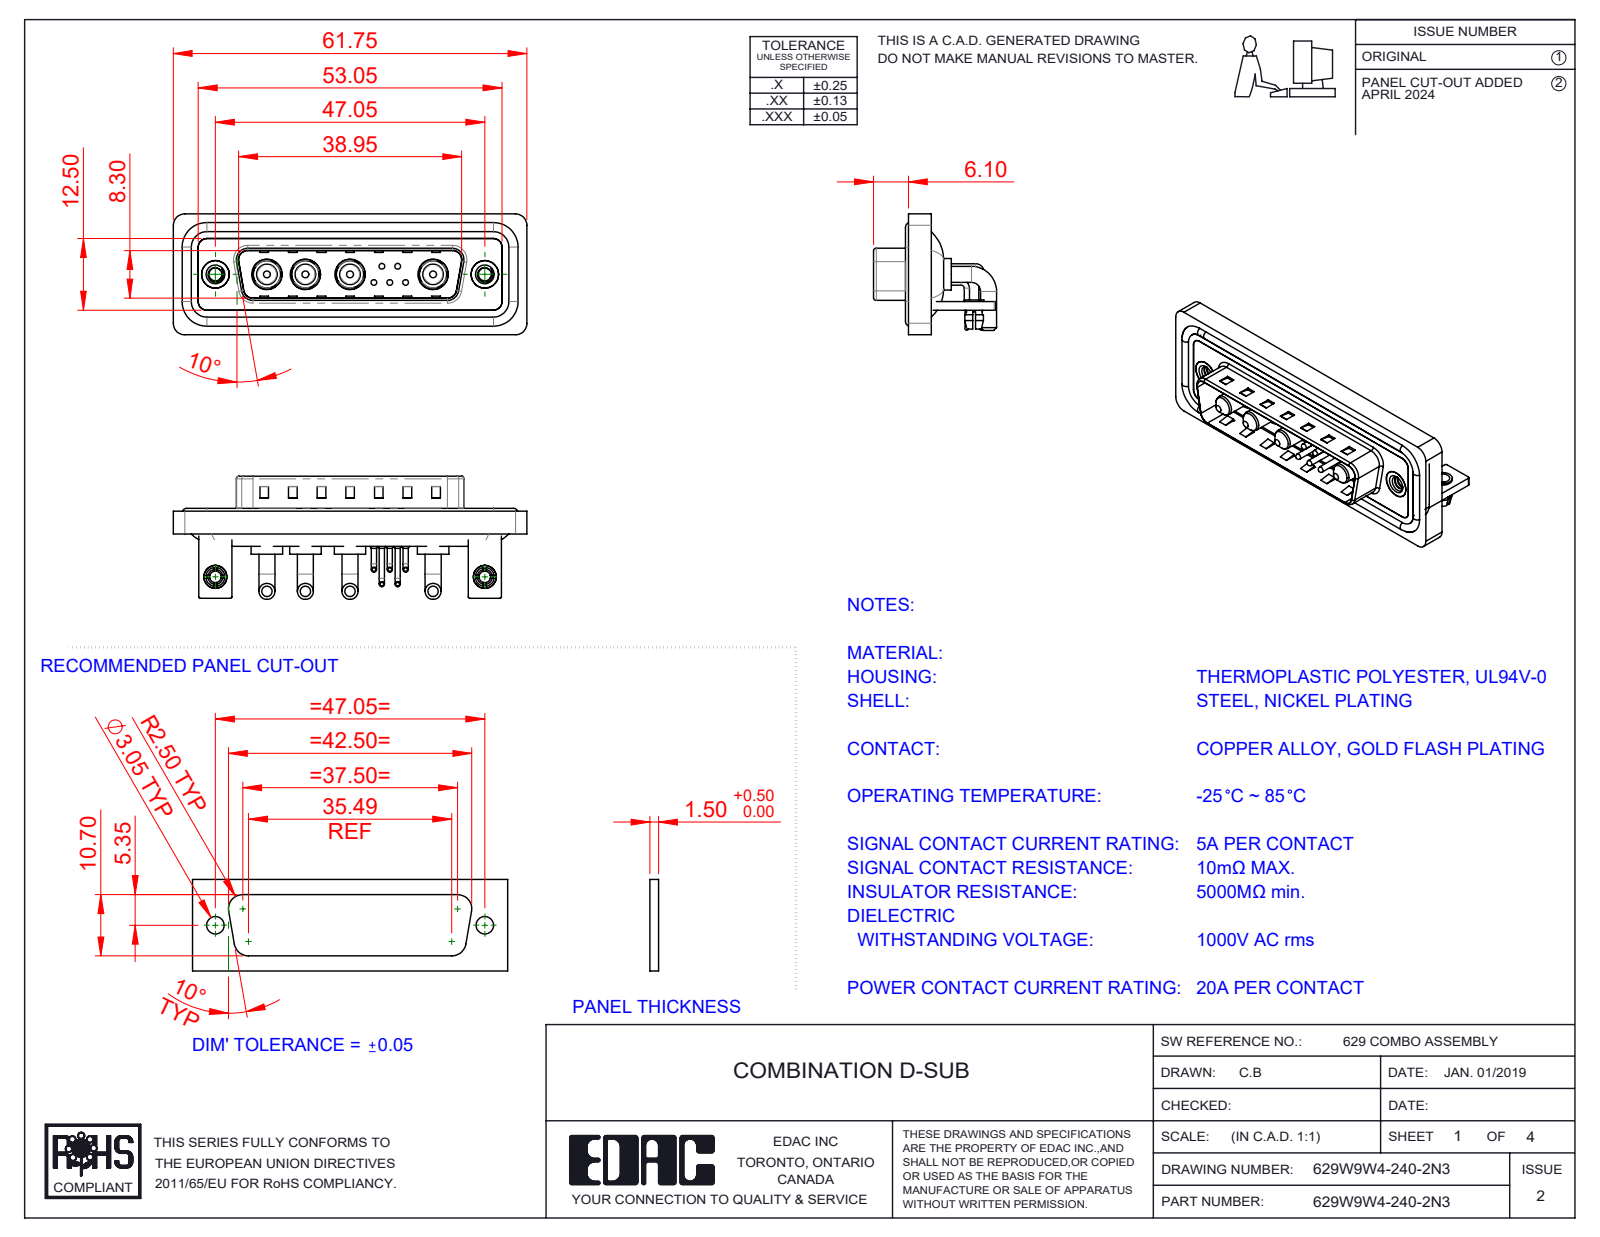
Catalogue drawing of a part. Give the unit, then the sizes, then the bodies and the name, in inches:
Units: inches
Overall size (bounding box): 2.431 × 0.846 × 0.831
Round holes (diameter × count): ⌀0.079 ×7, ⌀0.03 ×5, ⌀0.063 ×5, ⌀0.191 ×4, ⌀0.209 ×4, ⌀0.089 ×2, ⌀0.098 ×2, ⌀0.126 ×2, ⌀0.157 ×2, ⌀0.189 ×2, ⌀0.197 ×2
Round bosses / shafts (diameter × count): ⌀0.035 ×10, ⌀0.11 ×8, ⌀0.059 ×5, ⌀0.039 ×5, ⌀0.026 ×5, ⌀0.217 ×4, ⌀0.205 ×4, ⌀0.187 ×4
Partial cylindrical surfaces — rounded edges, fillets, slot ends (radius × count): R0.079 ×19, R0.059 ×18, R0.01 ×16, R0.02 ×9, R0.063 ×8, R0.04 ×5, R0.024 ×4, R0.026 ×4
Main face-to-face distances: 0.016, 0.059, 0.031, 0.114, 0.083, 0.043, 0.146, 0.161, 0.177, 0.063
Hole centre spacings: 0.124, 0.109, 0.198, 0.571, 1.852, 0.109, 0.173, 0.174
Volume: 0.489 in³ · Surface area: 20.42 in²
Bodies: 24 solids, 1337 faces (637 planar, 502 cylindrical, 198 other)
Part name (STEP PRODUCT): 629Combo Threaded Rivet_3; 629Combo Housing_9W4; Power Pin_20A RA; 629Combo Contact Row 2 (+7 more)
STEP written by: SolidWorks 2023 (CONFIG_CONTROL_DESIGN)
